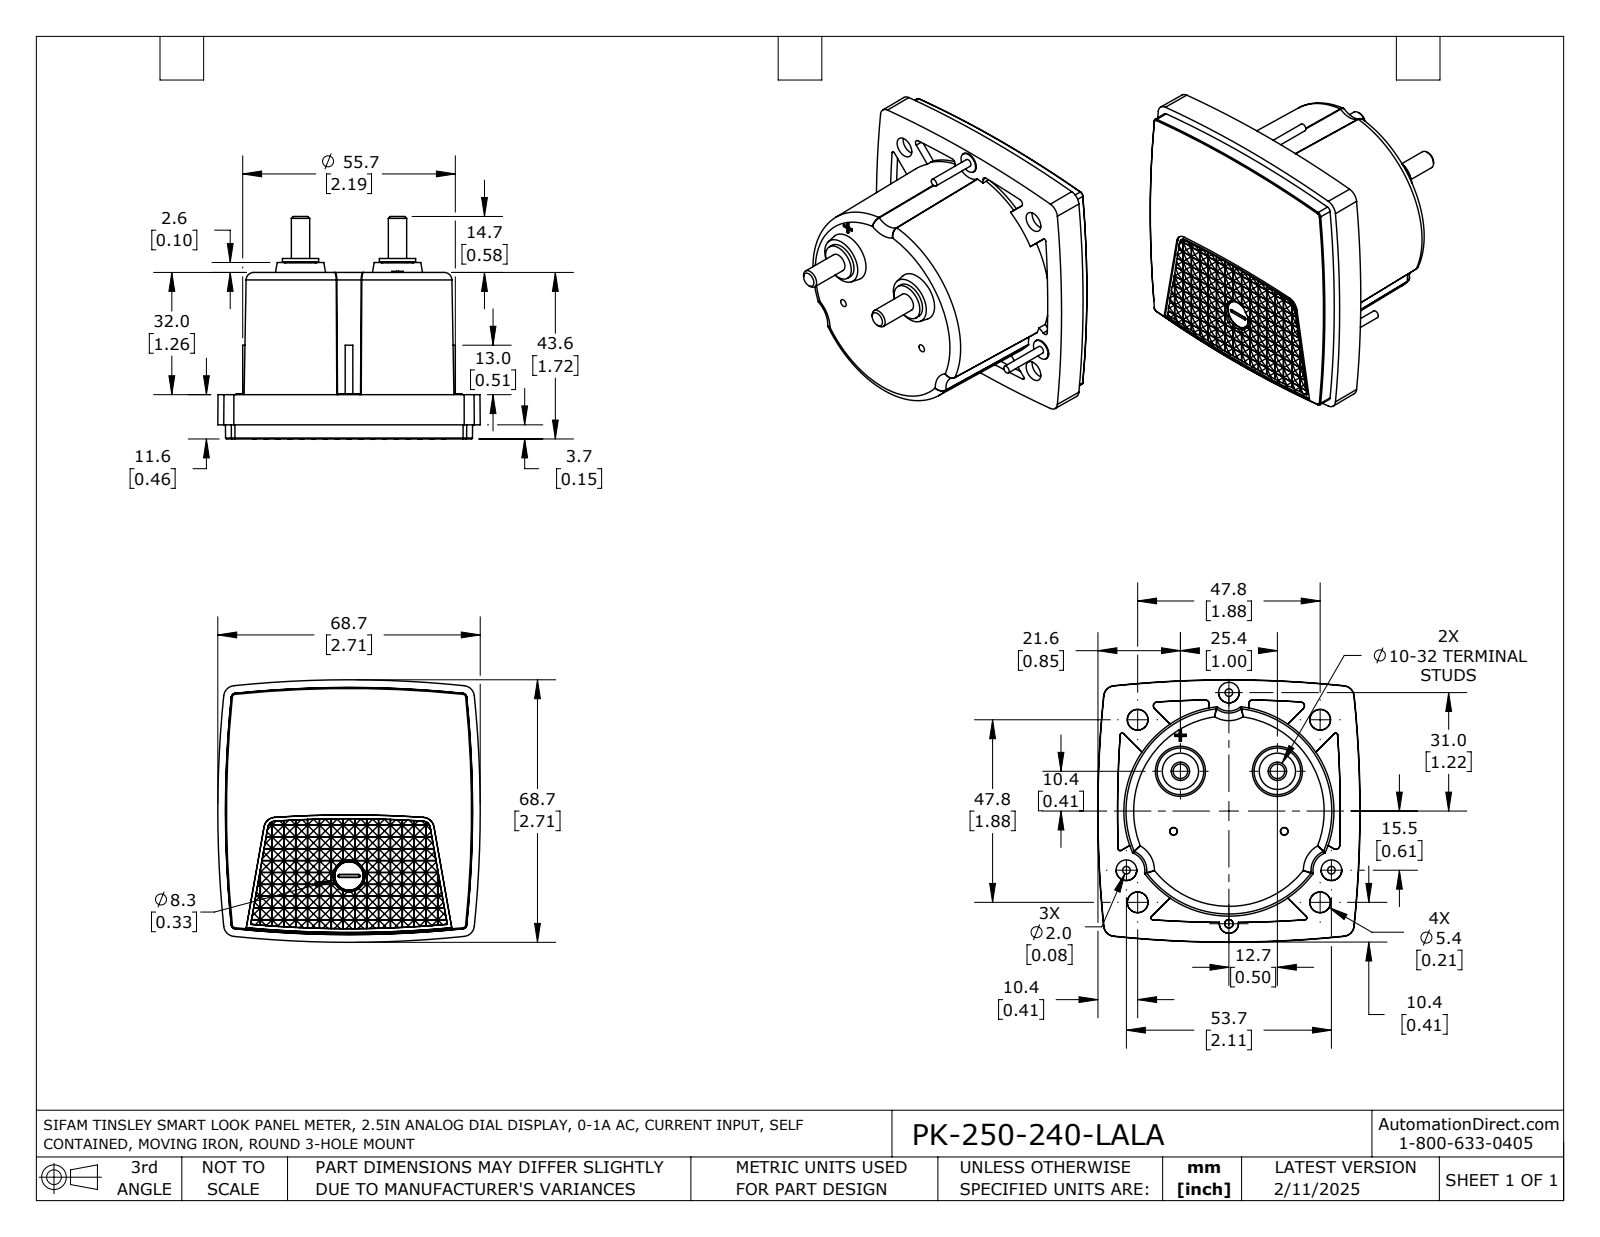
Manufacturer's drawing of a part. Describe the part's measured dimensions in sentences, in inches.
The part is named "PK-250-240-LALA". Its 3-D file was written by "SolidWorks 2021 (AUTOMOTIVE_DESIGN)". It is 1 solid with 1550 faces: 1165 planar, 265 cylindrical and 120 other. Overall it measures 2.706 by 2.706 by 2.297 inches. Its volume is 7.594 cubic inches and its surface area 30.41 square inches. Round bosses or shafts: 3 of diameter 0.213, 3 of diameter 0.079, 2 of diameter 0.374, 2 of diameter 0.189, 1 of diameter 0.215. Partial cylindrical surfaces (rounded edges, fillets, slot ends): 2 of radius 0.167, 1 of radius 1.083. The main face-to-face distances are 1.717, 1.26, 0.457, 0.024, 0.087, 0.096, 0.311, 0.12, 0.072, 1.346.
